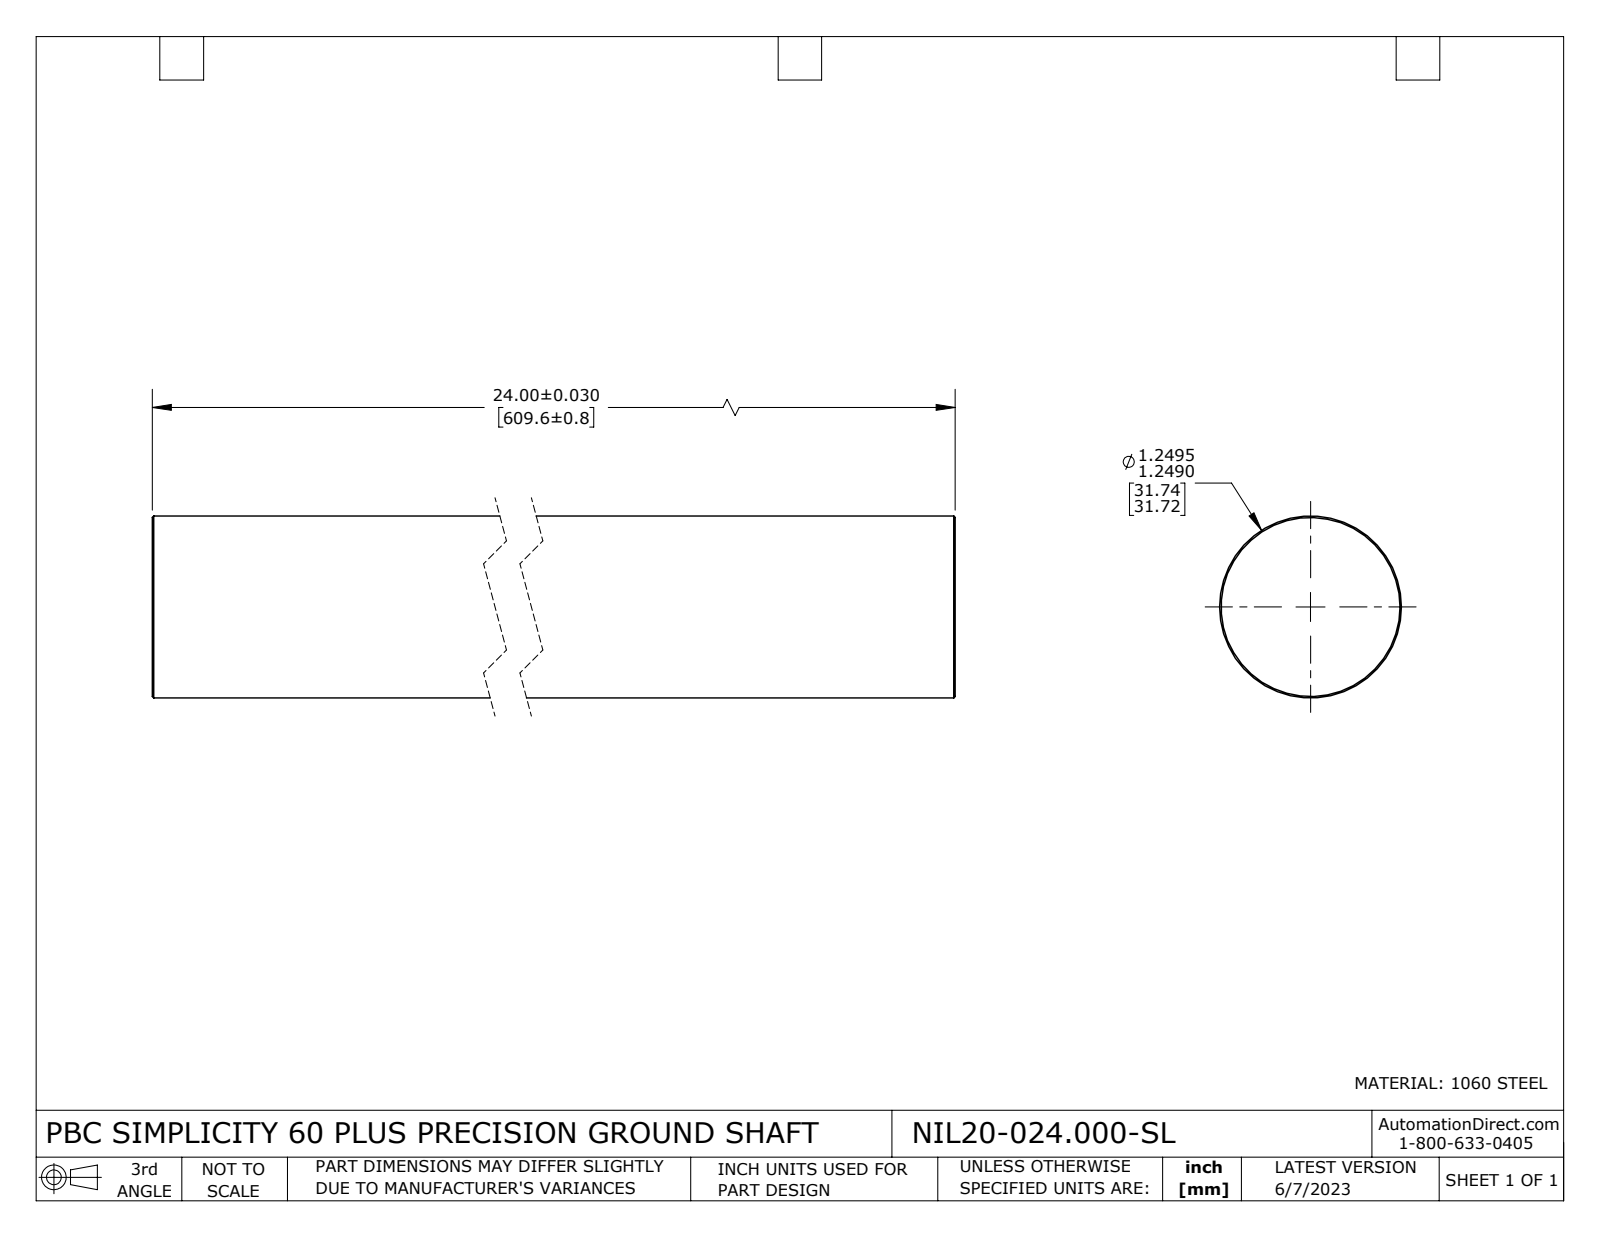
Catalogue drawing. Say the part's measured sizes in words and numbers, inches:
The part is named "NIL20-024.000-SL". Its 3-D file was written by "SolidWorks 2021 (CONFIG_CONTROL_DESIGN)". It is 1 solid with 8 faces: 2 planar, 2 cylindrical and 4 other. Overall it measures 24 by 1.25 by 1.25 inches. Its volume is 29.45 cubic inches and its surface area 96.66 square inches. Round bosses or shafts: 1 of diameter 1.25. The main face-to-face distances are 24.
